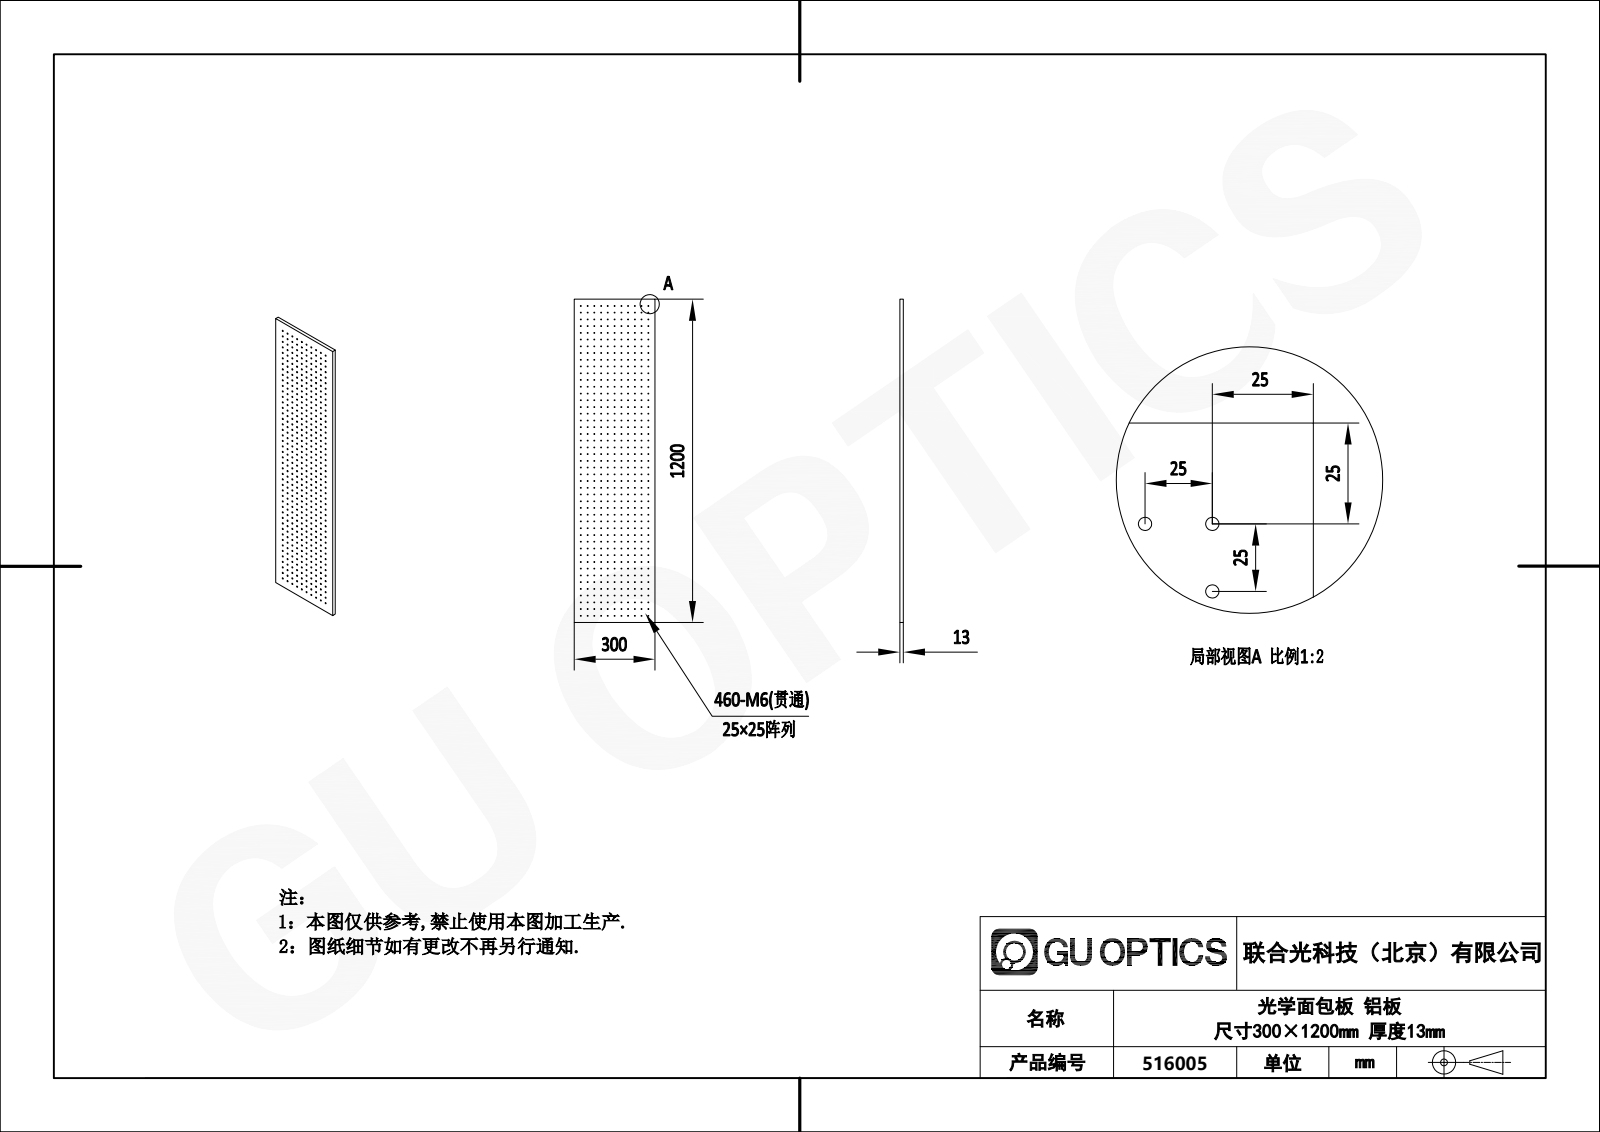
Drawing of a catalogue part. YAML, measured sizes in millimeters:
part_name: "516005"
step_written_by: "SolidWorks 2020 (CONFIG_CONTROL_DESIGN)"
units: millimeters
bodies: {solids: 1, faces: 1040, planar: 6, cylindrical: 1034, other: 0}
overall_size: [1200, 300, 13]
volume: 4548000
surface_area: 844271
round_holes:
  - {diameter: 5, count: 517}
face_to_face_distances: [13, 300, 1200]
hole_center_spacings: [25, 50, 75, 100, 125, 150, 175, 200]
